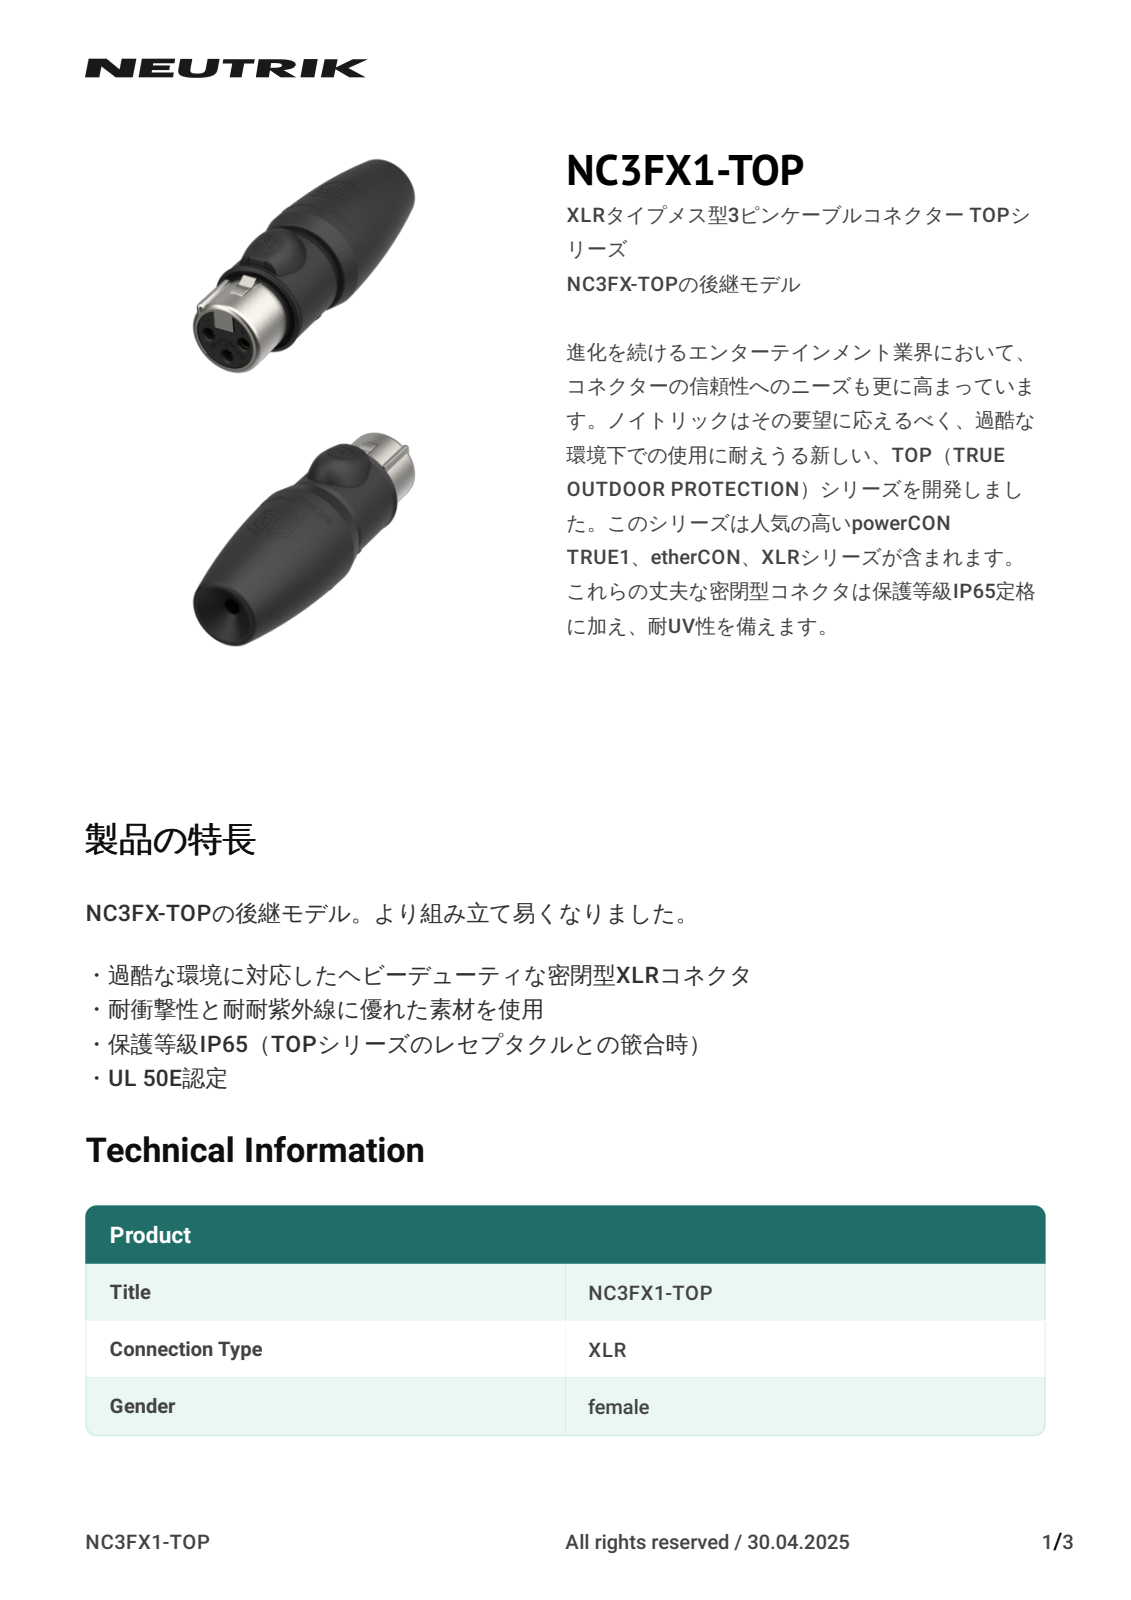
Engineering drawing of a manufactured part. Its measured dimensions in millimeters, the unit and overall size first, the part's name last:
Units: millimetres
Overall size (bounding box): 65.62 × 24.39 × 22.52
Round holes (diameter × count): ⌀2.5 ×3, ⌀2.55 ×3, ⌀5.13 ×1, ⌀13 ×1
Round bosses / shafts (diameter × count): ⌀19.35 ×1, ⌀15.75 ×1, ⌀6 ×1
Partial cylindrical surfaces — rounded edges, fillets, slot ends (radius × count): R0.22 ×9, R1 ×4, R0.2 ×2, R0.75 ×2, R0.3 ×1, R0.5 ×1, R1.59 ×1, R2.02 ×1
Main face-to-face distances: 29.08, 29.28, 4.16, 3.1, 3, 4.36, 24.92, 62.08, 61.88, 57.72
Hole centre spacings: 4.05, 5.66, 3.95, 8.1
Volume: 18 851 mm³ · Surface area: 4 873 mm²
Bodies: 1 solid, 1222 faces (577 planar, 85 cylindrical, 560 other)
Part name (STEP PRODUCT): 30010117
STEP written by: CREO PARAMETRIC BY PTC INC, 2021184 (CONFIG_CONTROL_DESIGN)
